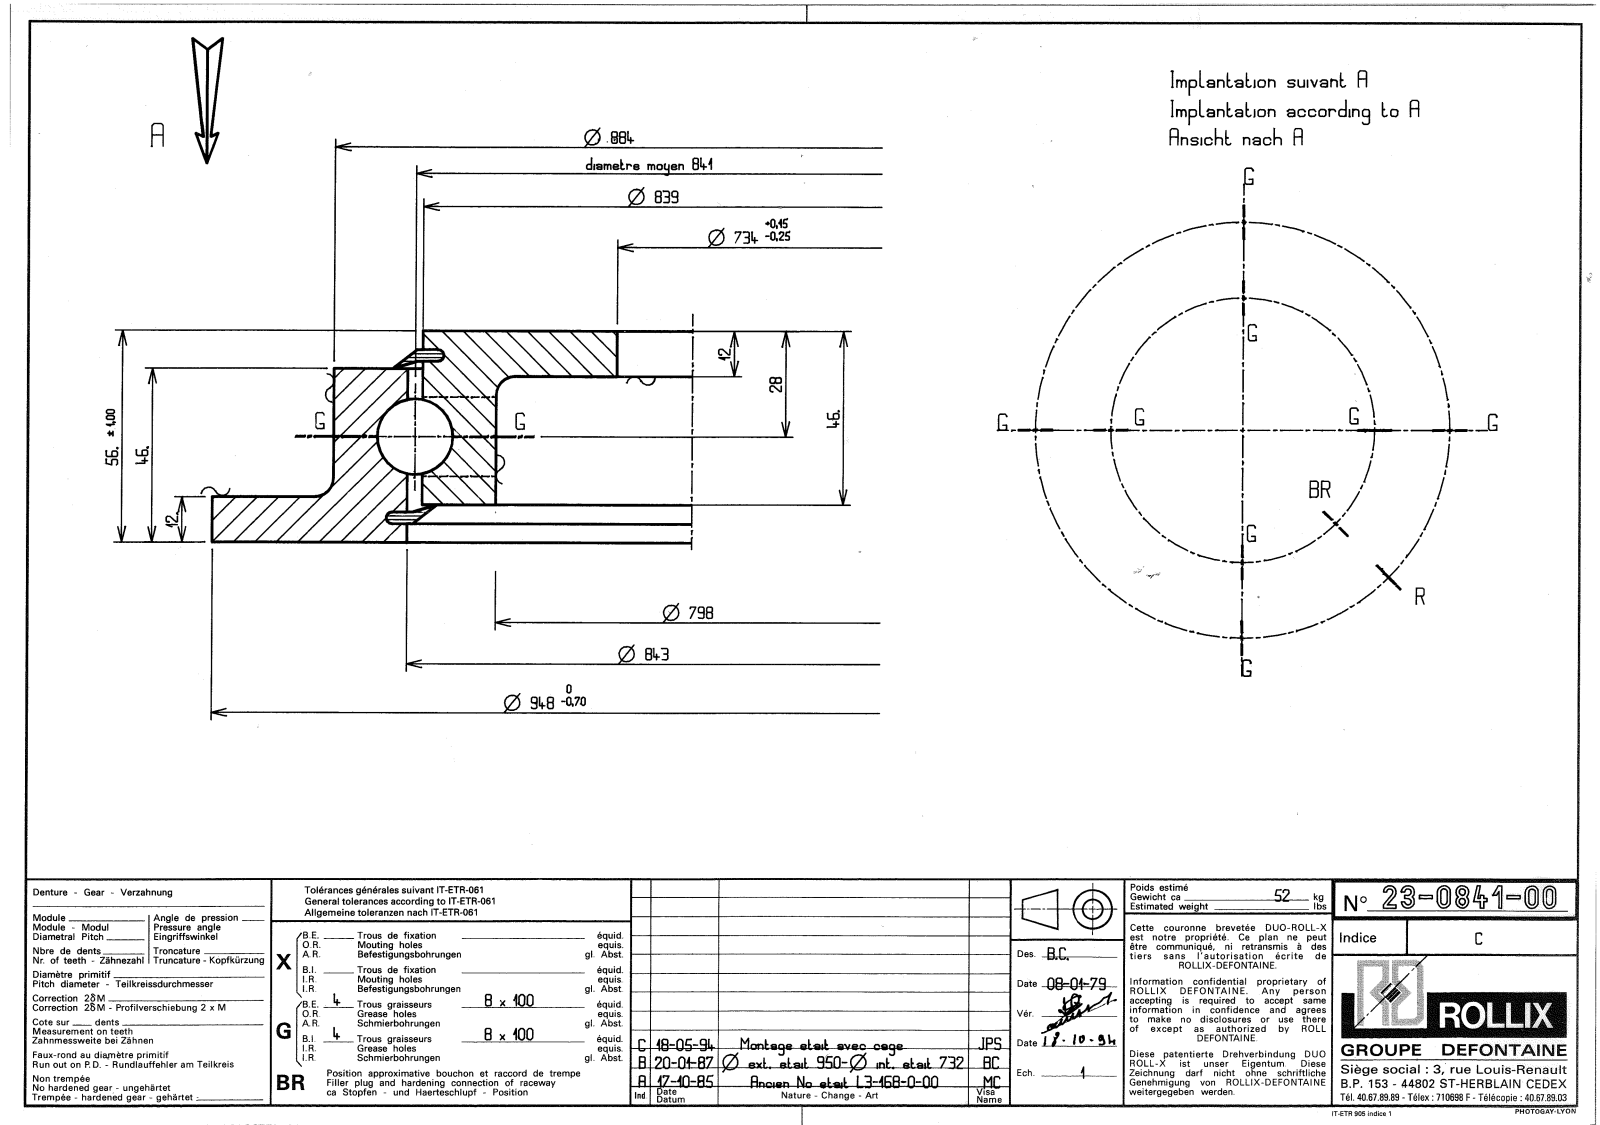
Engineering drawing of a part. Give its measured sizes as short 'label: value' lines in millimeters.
name: 23-0841-00
written by: SolidWorks 2016 (CONFIG_CONTROL_DESIGN)
unit: mm
bodies: 13 solids, 258 faces (94 planar, 52 cylindrical, 112 other)
size: 948 × 948 × 56
volume: 6 265 000 mm³; area: 1 264 000 mm²
holes: 8× ⌀7, 1× ⌀734, 1× ⌀798, 1× ⌀845.5
bosses: 8× ⌀8, 1× ⌀948, 1× ⌀884, 1× ⌀836.5
face distances: 12, 44, 56, 10, 46, 2, 34, 32, 36, 8.05
hole spacings: 0.37, 0.52
